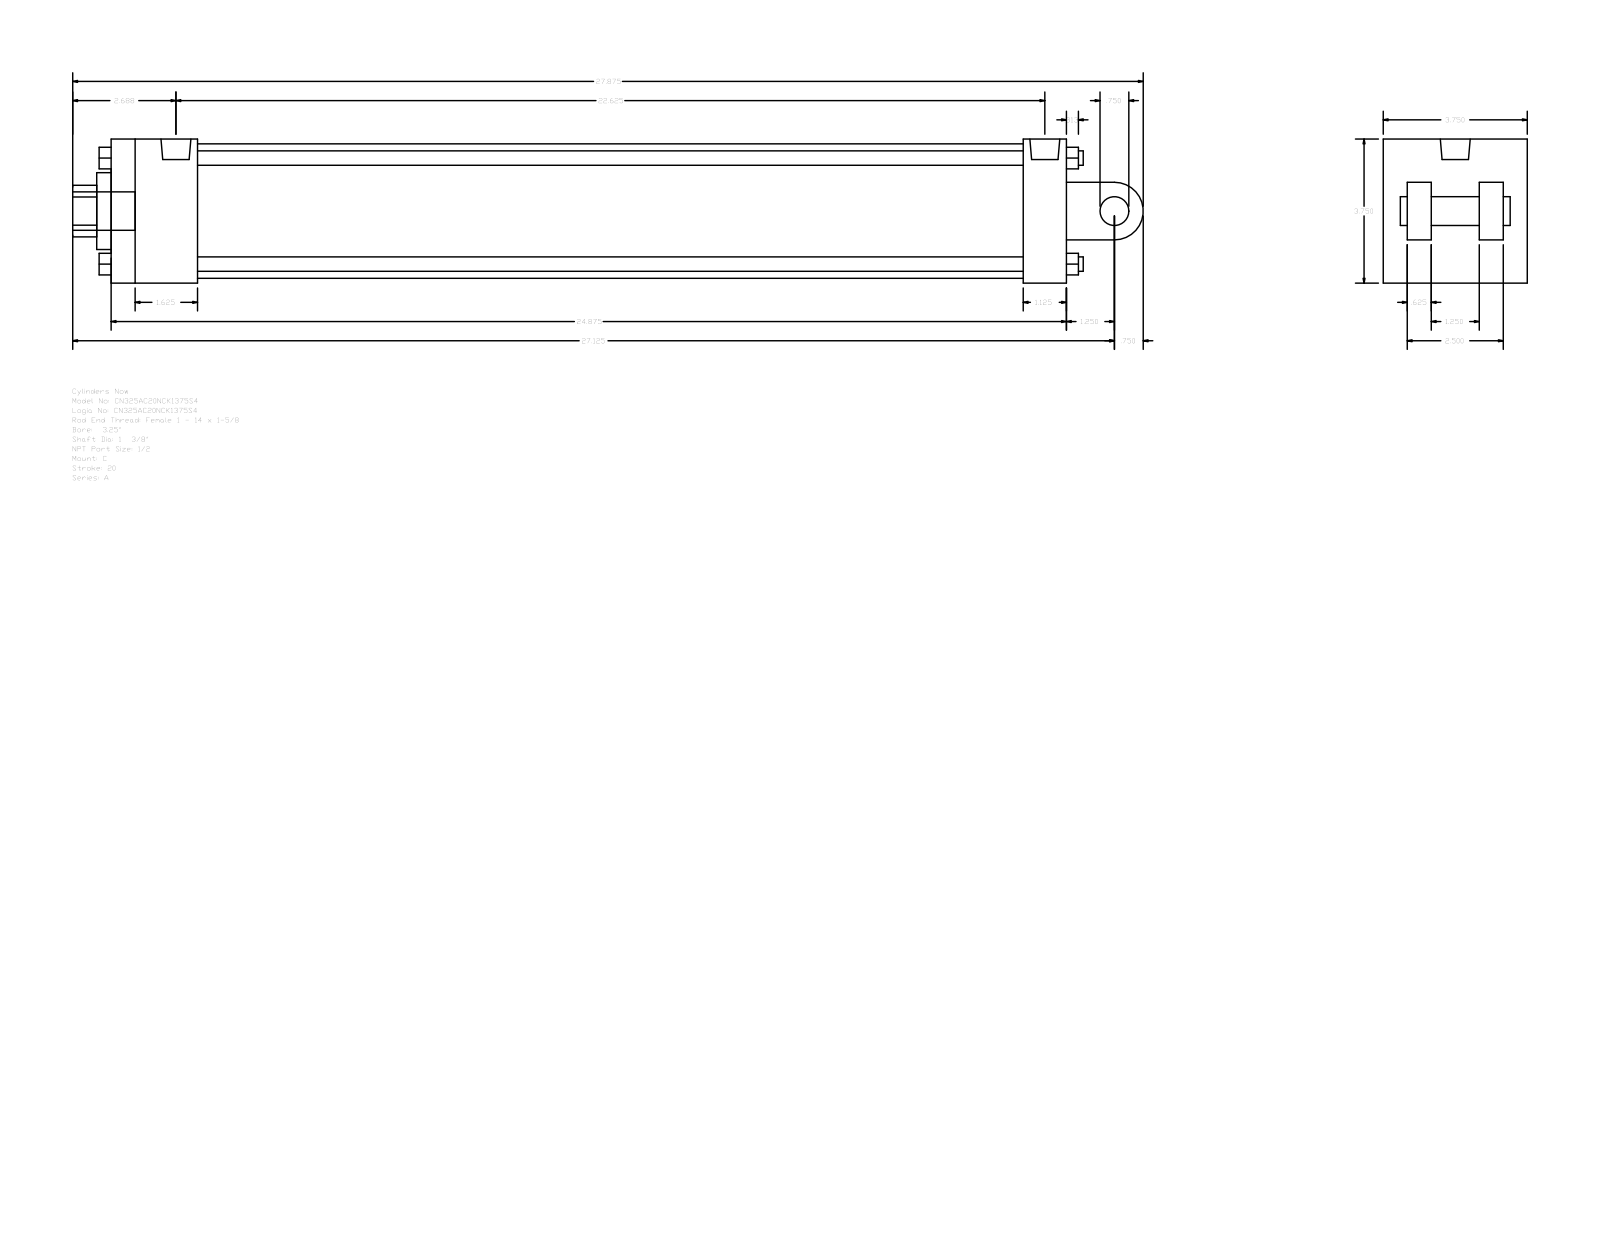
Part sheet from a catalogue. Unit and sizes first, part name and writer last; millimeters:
Units: millimetres
Overall size (bounding box): 708.02 × 95.25 × 95.25
Round holes (diameter × count): ⌀8.73 ×2, ⌀19.77 ×1, ⌀34.92 ×1, ⌀50.8 ×1, ⌀88.9 ×1
Round bosses / shafts (diameter × count): ⌀9.53 ×4, ⌀8.73 ×2, ⌀25.4 ×1, ⌀19.77 ×1, ⌀19.05 ×1
Partial cylindrical surfaces — rounded edges, fillets, slot ends (radius × count): R17.06 ×1, R19.05 ×1
Main face-to-face distances: 95.24, 15.87, 631.83, 63.5, 66.67, 28.58, 31.74, 79.37, 47.63, 603.25
Hole centre spacings: 3.18
Bodies: 0 solids, 135 faces (102 planar, 33 cylindrical, 0 other)
Part name (STEP PRODUCT): A_C__0325_1.375
STEP written by: GSSL Pune (CONFIG_CONTROL_DESIGN)
